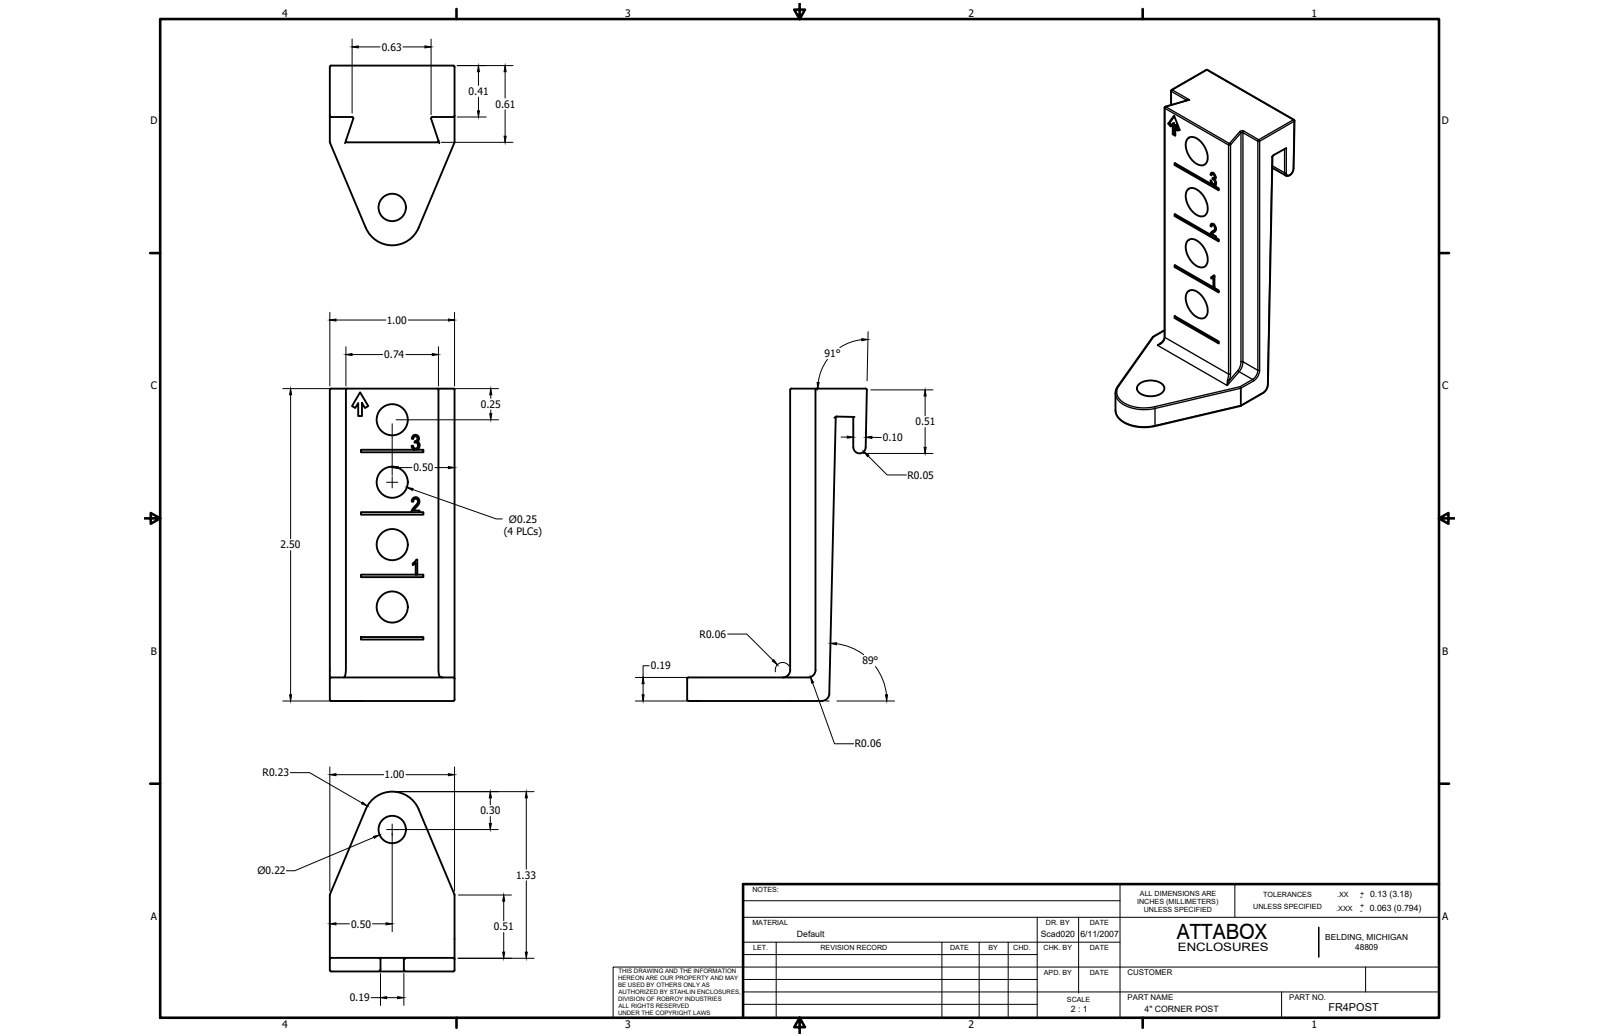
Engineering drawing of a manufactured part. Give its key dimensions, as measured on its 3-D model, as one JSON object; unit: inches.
{"part_name": "FR4POST", "step_written_by": "SolidWorks 2019 (AUTOMOTIVE_DESIGN)", "units": "inches", "bodies": {"solids": 12, "faces": 776, "planar": 328, "cylindrical": 224, "other": 224}, "overall_size": [6.556, 6.556, 2.703], "volume_in3": 3.417, "surface_area_in2": 47.94, "round_holes": [[0.25, 16], [0.217, 4], [0.22, 4]], "round_bosses_or_shafts": [[0.433, 4], [0.373, 4], [0.19, 4]], "partial_cylinders_radius": [[0.01, 160], [0.06, 12], [0.049, 4], [0.23, 4]], "face_to_face_distances": [3.027, 4.027, 0.203, 3.23, 4.23, 7.256, 7.054, 0.188, 2.314, 2.502], "hole_center_spacings": [0.5, 1, 1.5, 4.25, 4.25, 4.25, 6.01, 6.01]}
